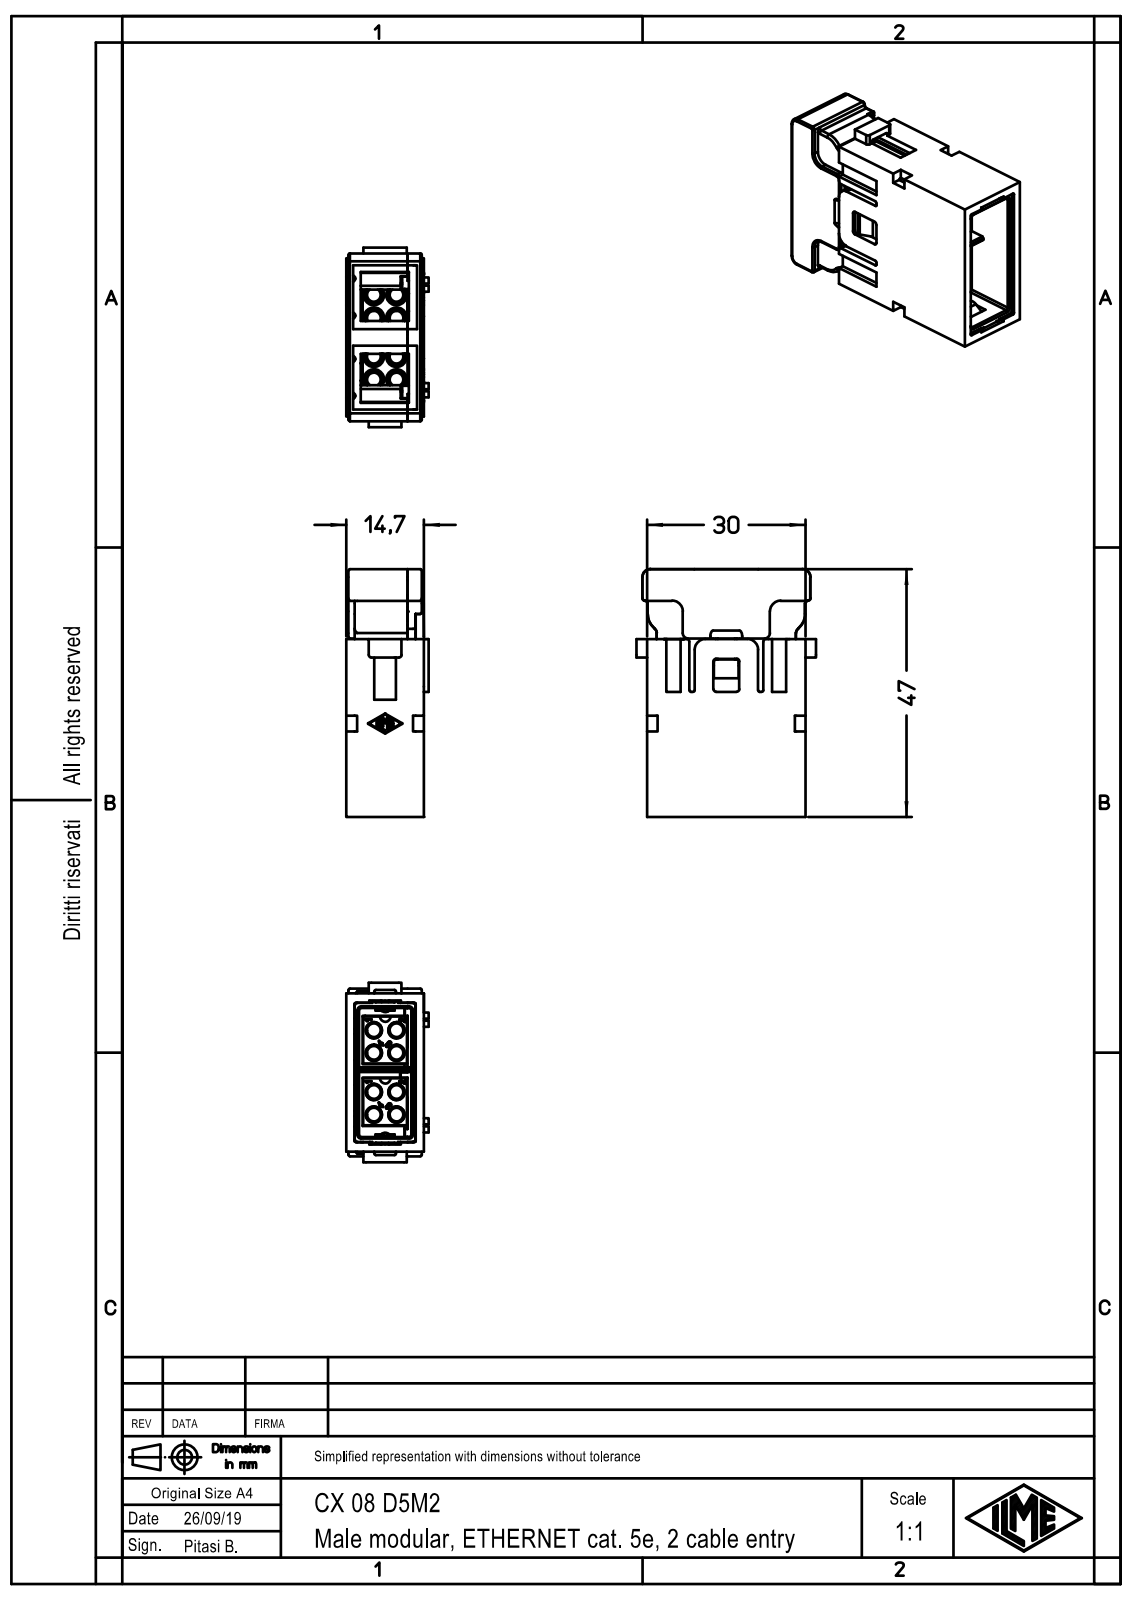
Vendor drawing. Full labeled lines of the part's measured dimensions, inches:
Part name (STEP PRODUCT): CX 08 D5M2
STEP written by: Creo Elements/Direct Modeling 20.1B 02-Apr-2019 (C) Parametric Technology GmbH (AUTOMOTIVE_DESIGN)
Units: inches
Bodies: 1 solid, 658 faces (386 planar, 203 cylindrical, 69 other)
Overall size (bounding box): 1.848 × 1.339 × 0.614
Volume: 0.921 in³ · Surface area: 19.81 in²
Round holes (diameter × count): ⌀0.102 ×10, ⌀0.089 ×2, ⌀0.197 ×2, ⌀0.055 ×1
Round bosses / shafts (diameter × count): ⌀0.185 ×2, ⌀0.075 ×2, ⌀0.051 ×1
Partial cylindrical surfaces — rounded edges, fillets, slot ends (radius × count): R0.02 ×46, R0.012 ×40, R0.016 ×8, R0.039 ×8, R0.079 ×6, R0.004 ×4, R0.008 ×4, R0.026 ×4
Main face-to-face distances: 0.063, 0.516, 0.061, 0.518, 0.455, 0.453, 0.457, 0.579, 0.016, 0.045
Hole centre spacings: 0.169, 0.239, 0.461, 0.491, 0.291, 0.337, 0.63, 0.652
